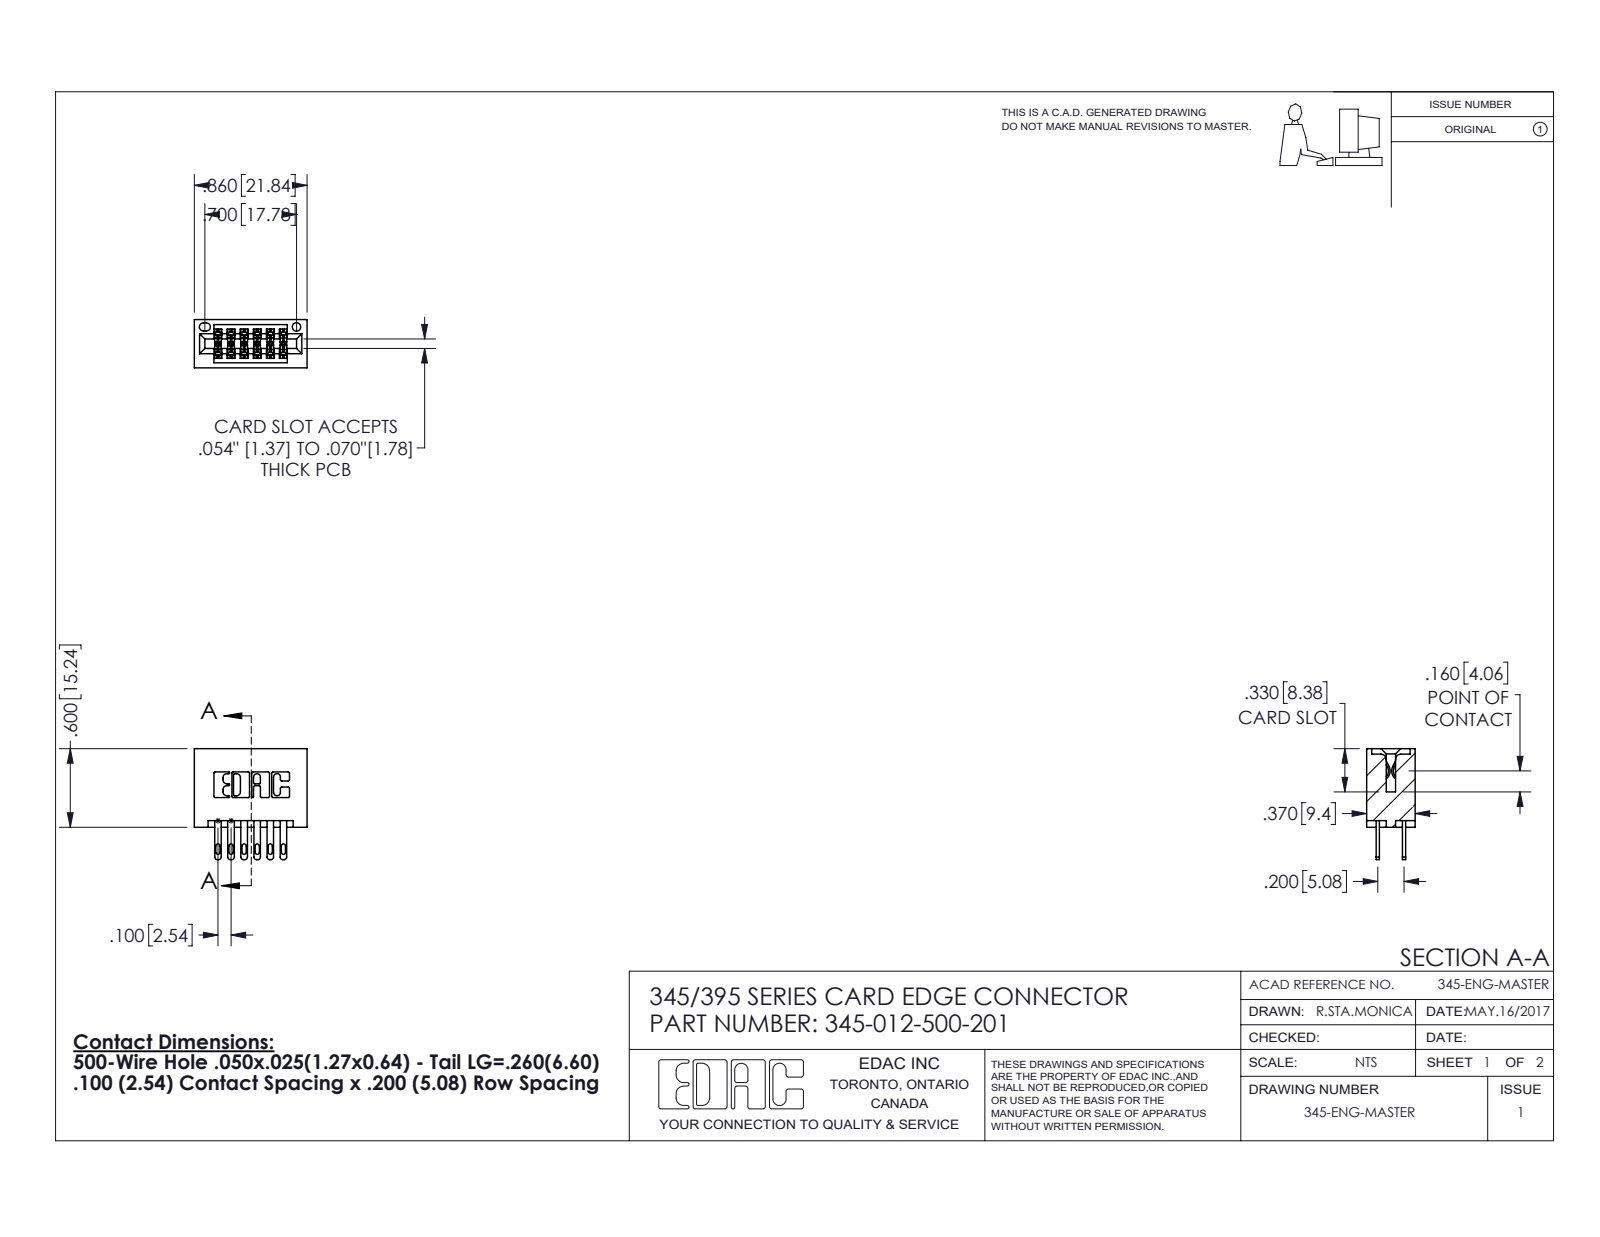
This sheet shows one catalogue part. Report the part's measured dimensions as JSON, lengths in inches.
{"part_name": "345-292-001_345-293-100; 345-012-500-201; 345 Part_No Mounting Lugs", "step_written_by": "SolidWorks 2016 (CONFIG_CONTROL_DESIGN)", "units": "inches", "bodies": {"solids": 13, "faces": 670, "planar": 400, "cylindrical": 270, "other": 0}, "overall_size": [0.86, 0.847, 0.37], "volume_in3": 0.149, "surface_area_in2": 5.17, "round_holes": [[0.064, 1]], "partial_cylinders_radius": [[0.01, 22], [0.006, 18], [0.016, 12], [0.02, 12], [0.007, 6], [0.031, 6], [0.026, 3], [0.014, 2]], "face_to_face_distances": [0.2, 0.298, 0.072, 0.1, 0.098, 0.272, 0.025, 0.37, 0.3, 0.225]}
